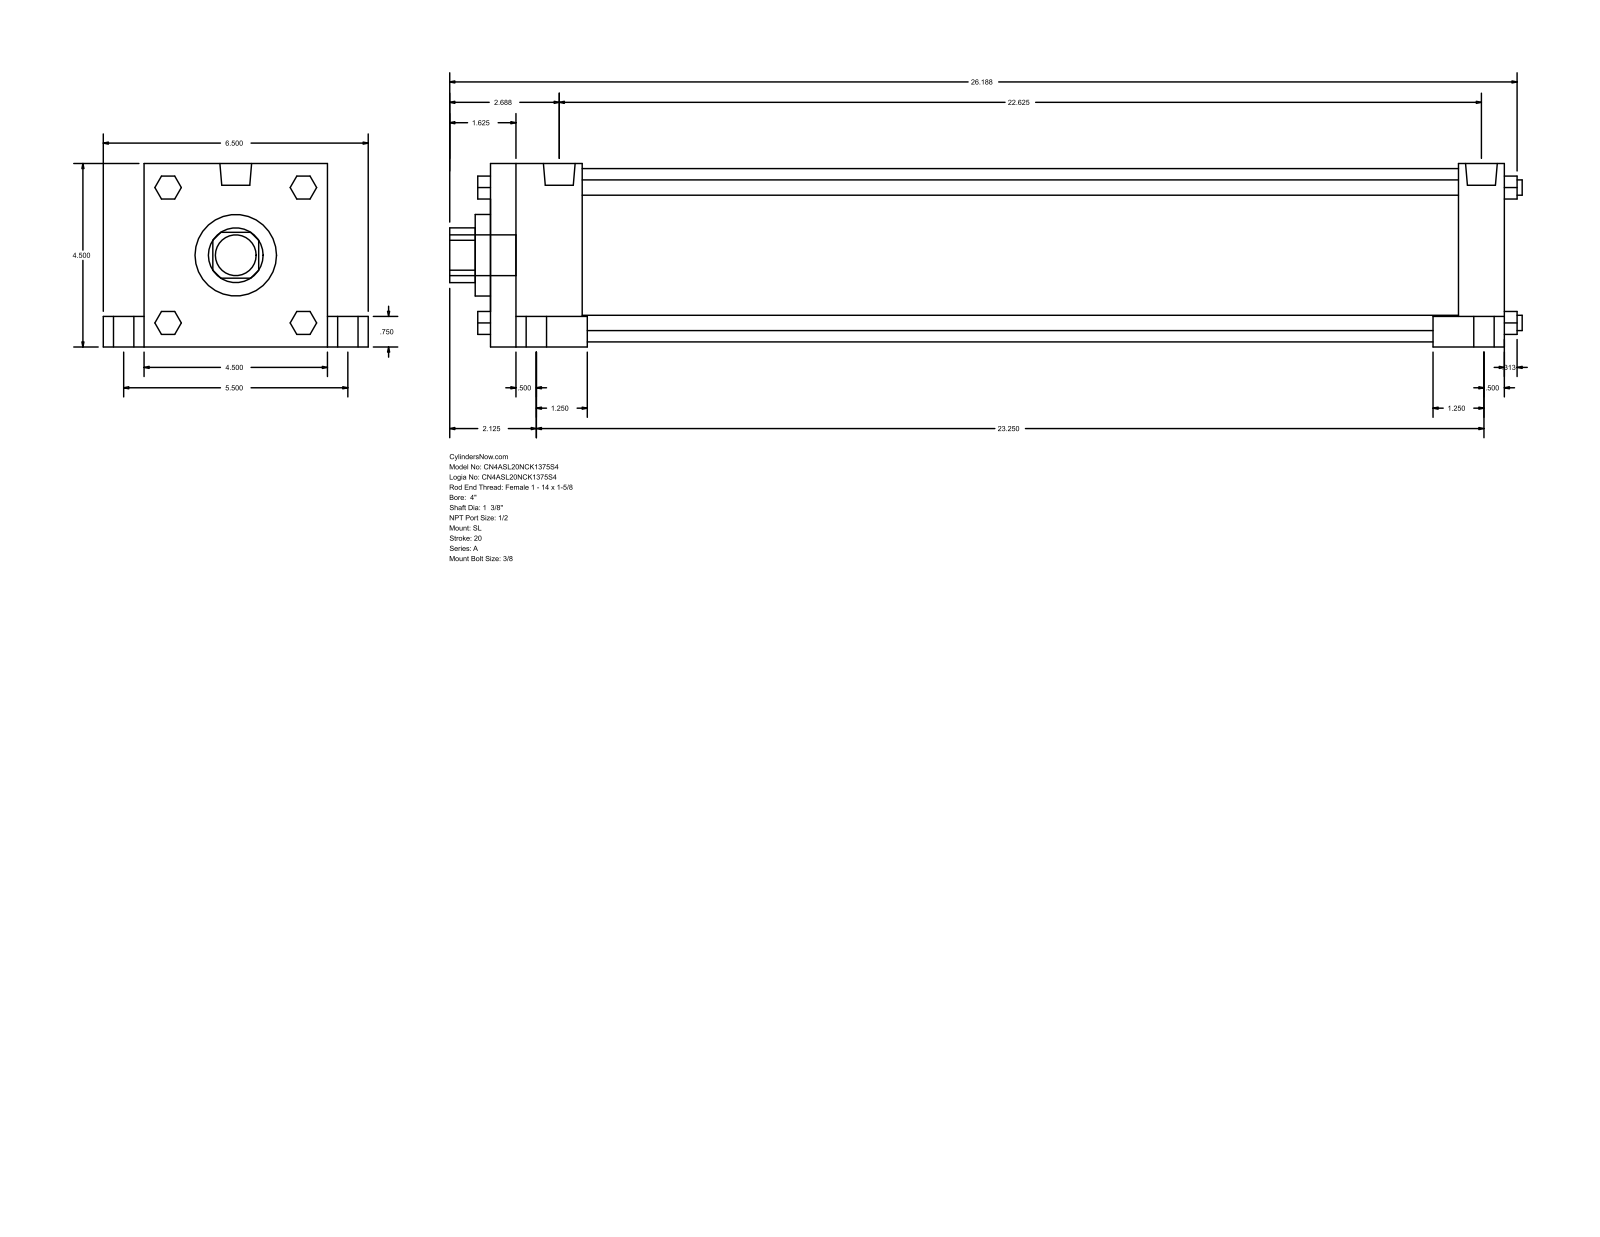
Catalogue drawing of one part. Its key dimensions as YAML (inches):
part_name: "A_SL__0400_1.375"
step_written_by: "GSSL Pune (CONFIG_CONTROL_DESIGN)"
units: inches
bodies: {solids: 0, faces: 150, planar: 114, cylindrical: 36, other: 0}
overall_size: [26.313, 6.5, 4.5]
round_holes:
  - {diameter: 1.375, count: 1}
  - {diameter: 2, count: 1}
  - {diameter: 4.25, count: 1}
round_bosses_or_shafts:
  - {diameter: 0.75, count: 4}
  - {diameter: 0.5, count: 4}
  - {diameter: 0.375, count: 4}
  - {diameter: 0.344, count: 4}
  - {diameter: 0.778, count: 2}
  - {diameter: 1, count: 1}
partial_cylinders:
  - {radius: 0.672, count: 1}
face_to_face_distances: [4.5, 24.875, 1.125, 1, 2.25, 22.625, 23.75, 21.5, 5.5, 0.75]
